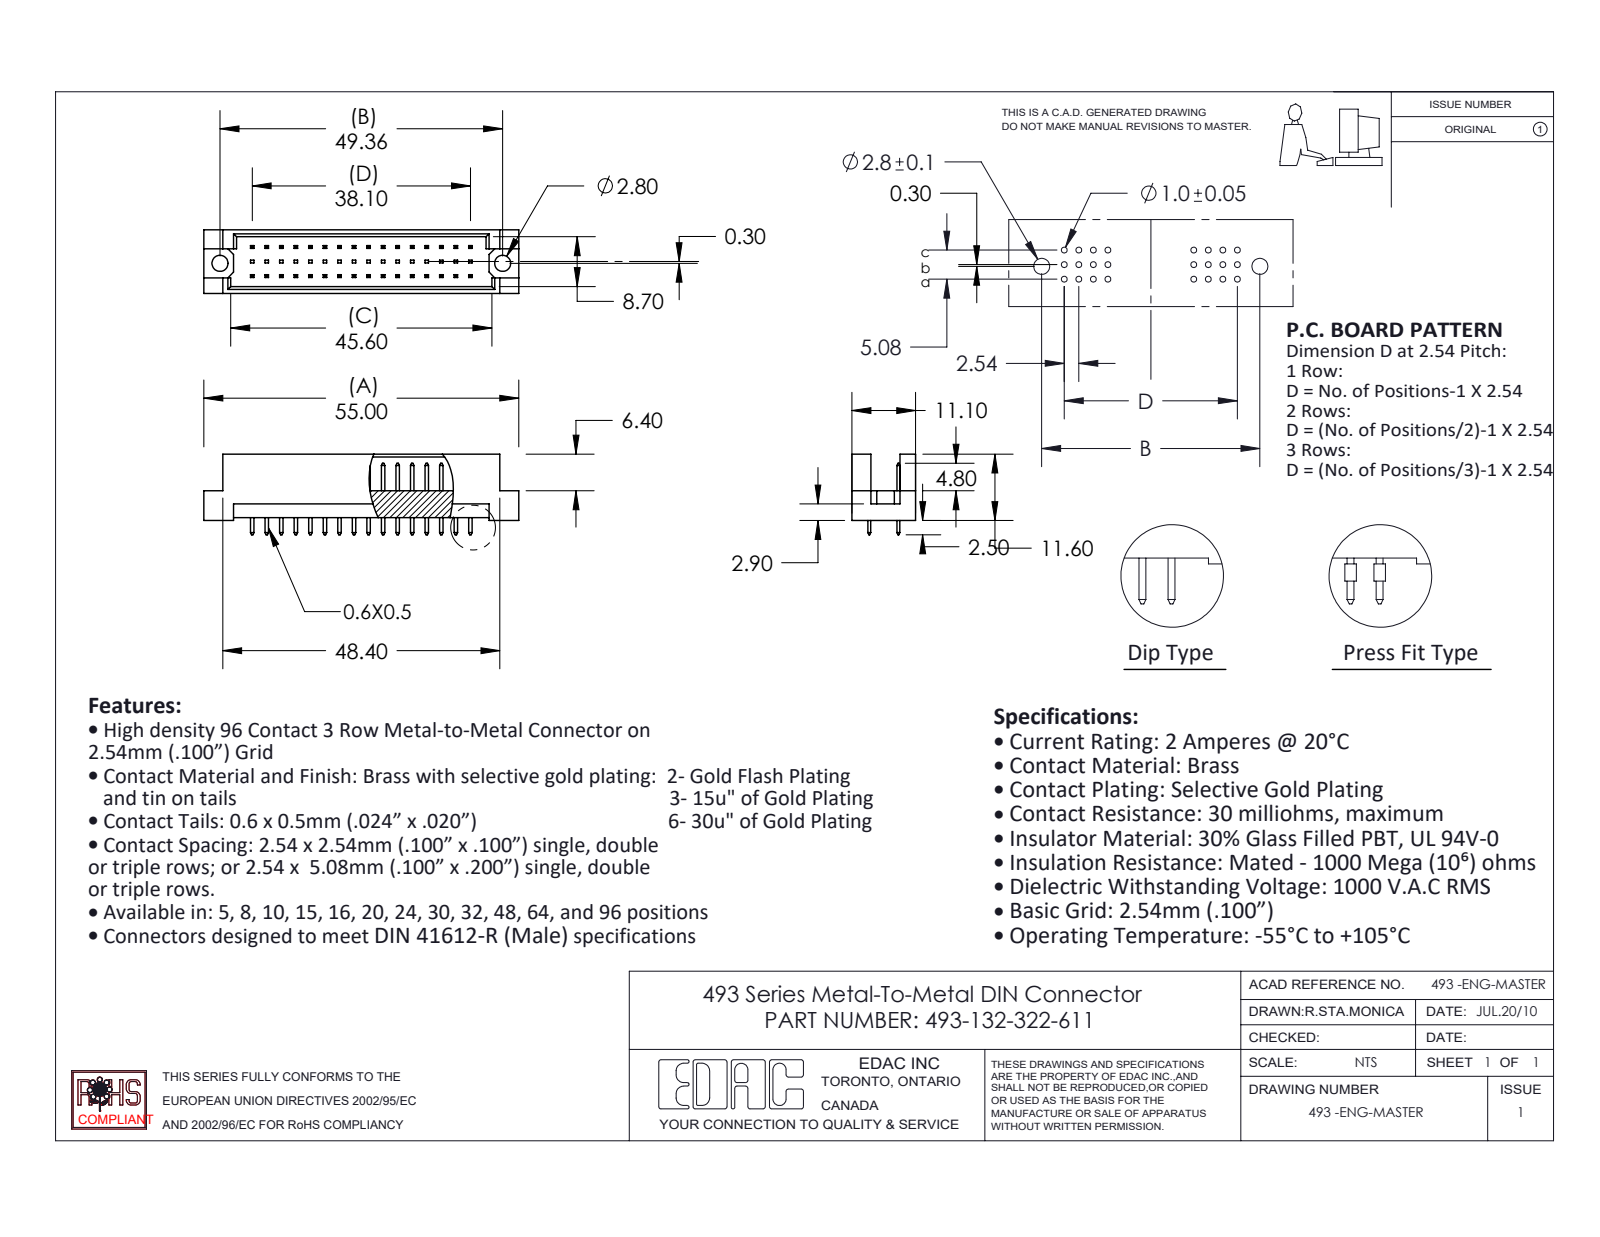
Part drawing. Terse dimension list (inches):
name: 493 Part_48; 493-290_22; 493-132-322-611
written by: SolidWorks 2020 (CONFIG_CONTROL_DESIGN)
unit: in
bodies: 33 solids, 692 faces (688 planar, 4 cylindrical, 0 other)
size: 2.165 × 0.555 × 0.437
volume: 0.207 in³; area: 7.167 in²
holes: 2× ⌀0.11
face distances: 0.047, 0.39, 0.2, 0.437, 0.02, 0.1, 0.343, 0.185, 0.109, 0.328
hole spacings: 1.943
